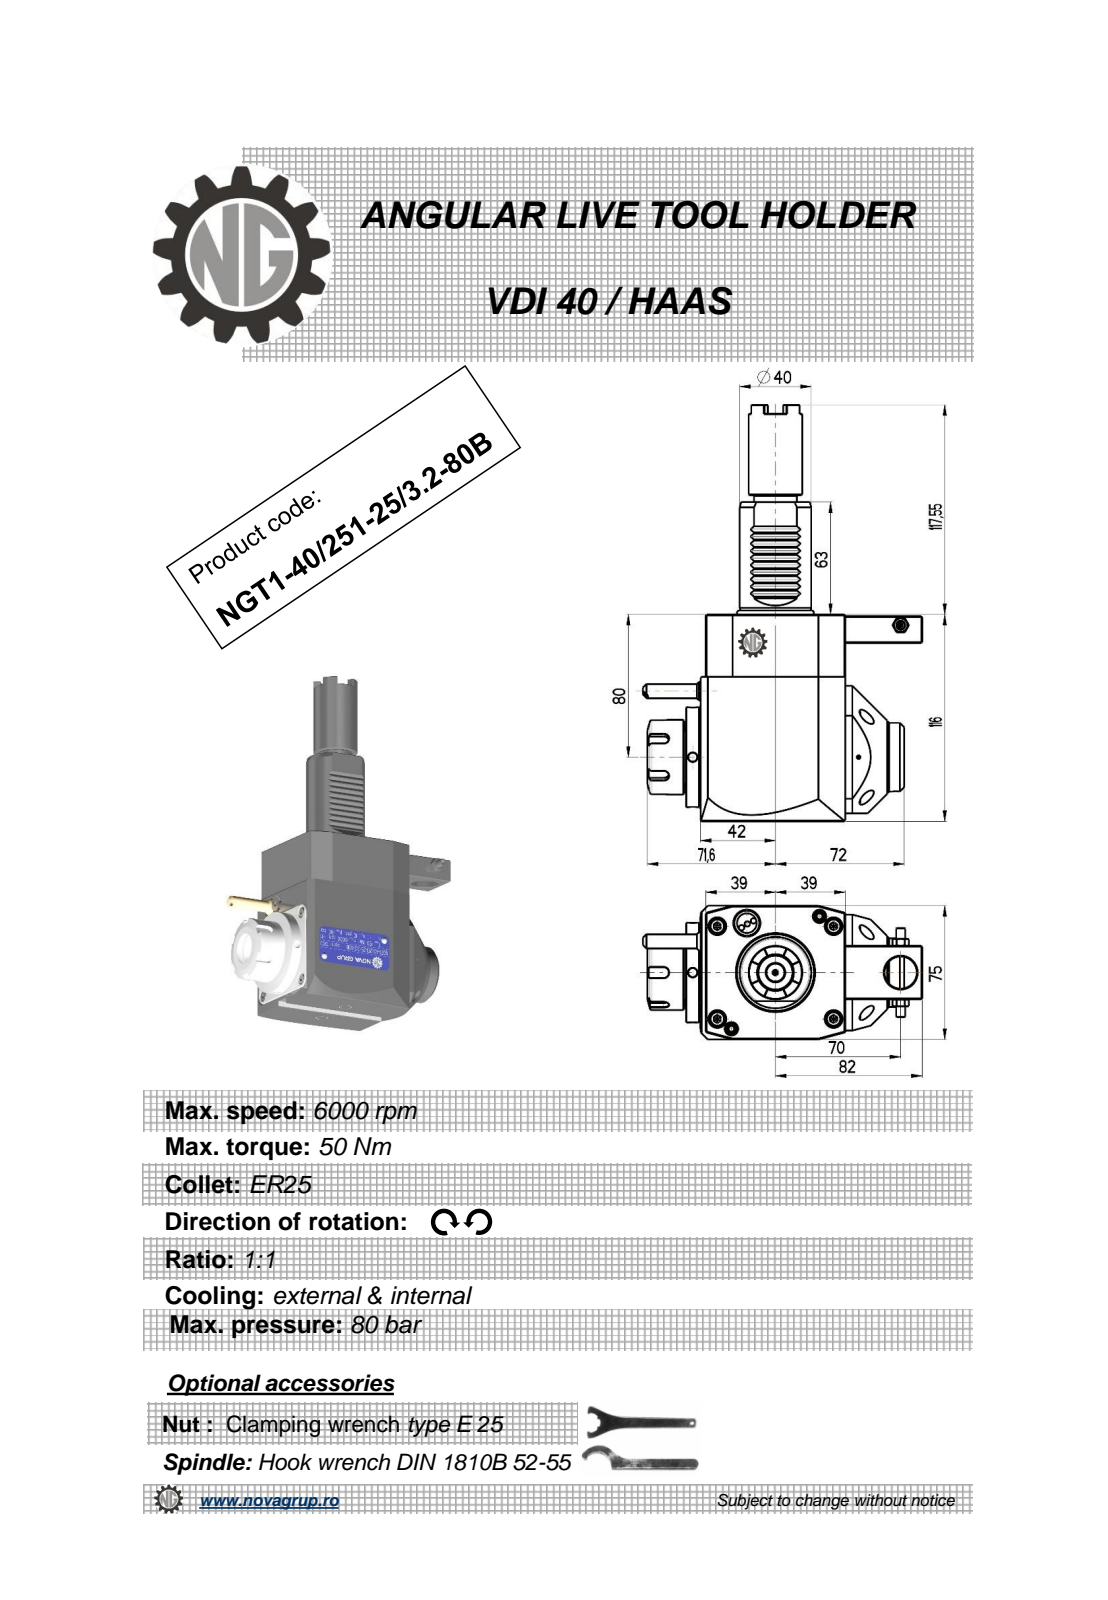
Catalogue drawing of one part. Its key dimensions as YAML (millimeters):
part_name: "NGT1_40_251_32_3_2_80B"
step_written_by: "PRO/ENGINEER BY PARAMETRIC TECHNOLOGY CORPORATION, 2010280 (CONFIG_CONTROL_DESIGN)"
units: millimeters
bodies: {solids: 1, faces: 491, planar: 224, cylindrical: 103, other: 164}
overall_size: [233.55, 156.14, 75]
volume: 934581
surface_area: 80574
round_holes:
  - {diameter: 5, count: 3}
  - {diameter: 3, count: 1}
  - {diameter: 4.2, count: 1}
  - {diameter: 9.5, count: 1}
  - {diameter: 18, count: 1}
  - {diameter: 20, count: 1}
  - {diameter: 20.3, count: 1}
  - {diameter: 38.8, count: 1}
  - {diameter: 42, count: 1}
round_bosses_or_shafts:
  - {diameter: 56, count: 1}
  - {diameter: 41.4, count: 1}
  - {diameter: 40, count: 1}
  - {diameter: 38.5, count: 1}
  - {diameter: 38.2, count: 1}
  - {diameter: 38, count: 1}
  - {diameter: 36, count: 1}
  - {diameter: 30, count: 1}
partial_cylinders:
  - {radius: 0.26, count: 12}
  - {radius: 0.3, count: 10}
  - {radius: 0.2, count: 6}
  - {radius: 3, count: 5}
  - {radius: 0.5, count: 1}
  - {radius: 40, count: 1}
face_to_face_distances: [75, 116, 3, 81, 78, 111, 11, 1, 2.8, 80.8]
hole_center_spacings: [39.58, 40.93, 46.25, 70, 72.5, 116.25, 137.8]
